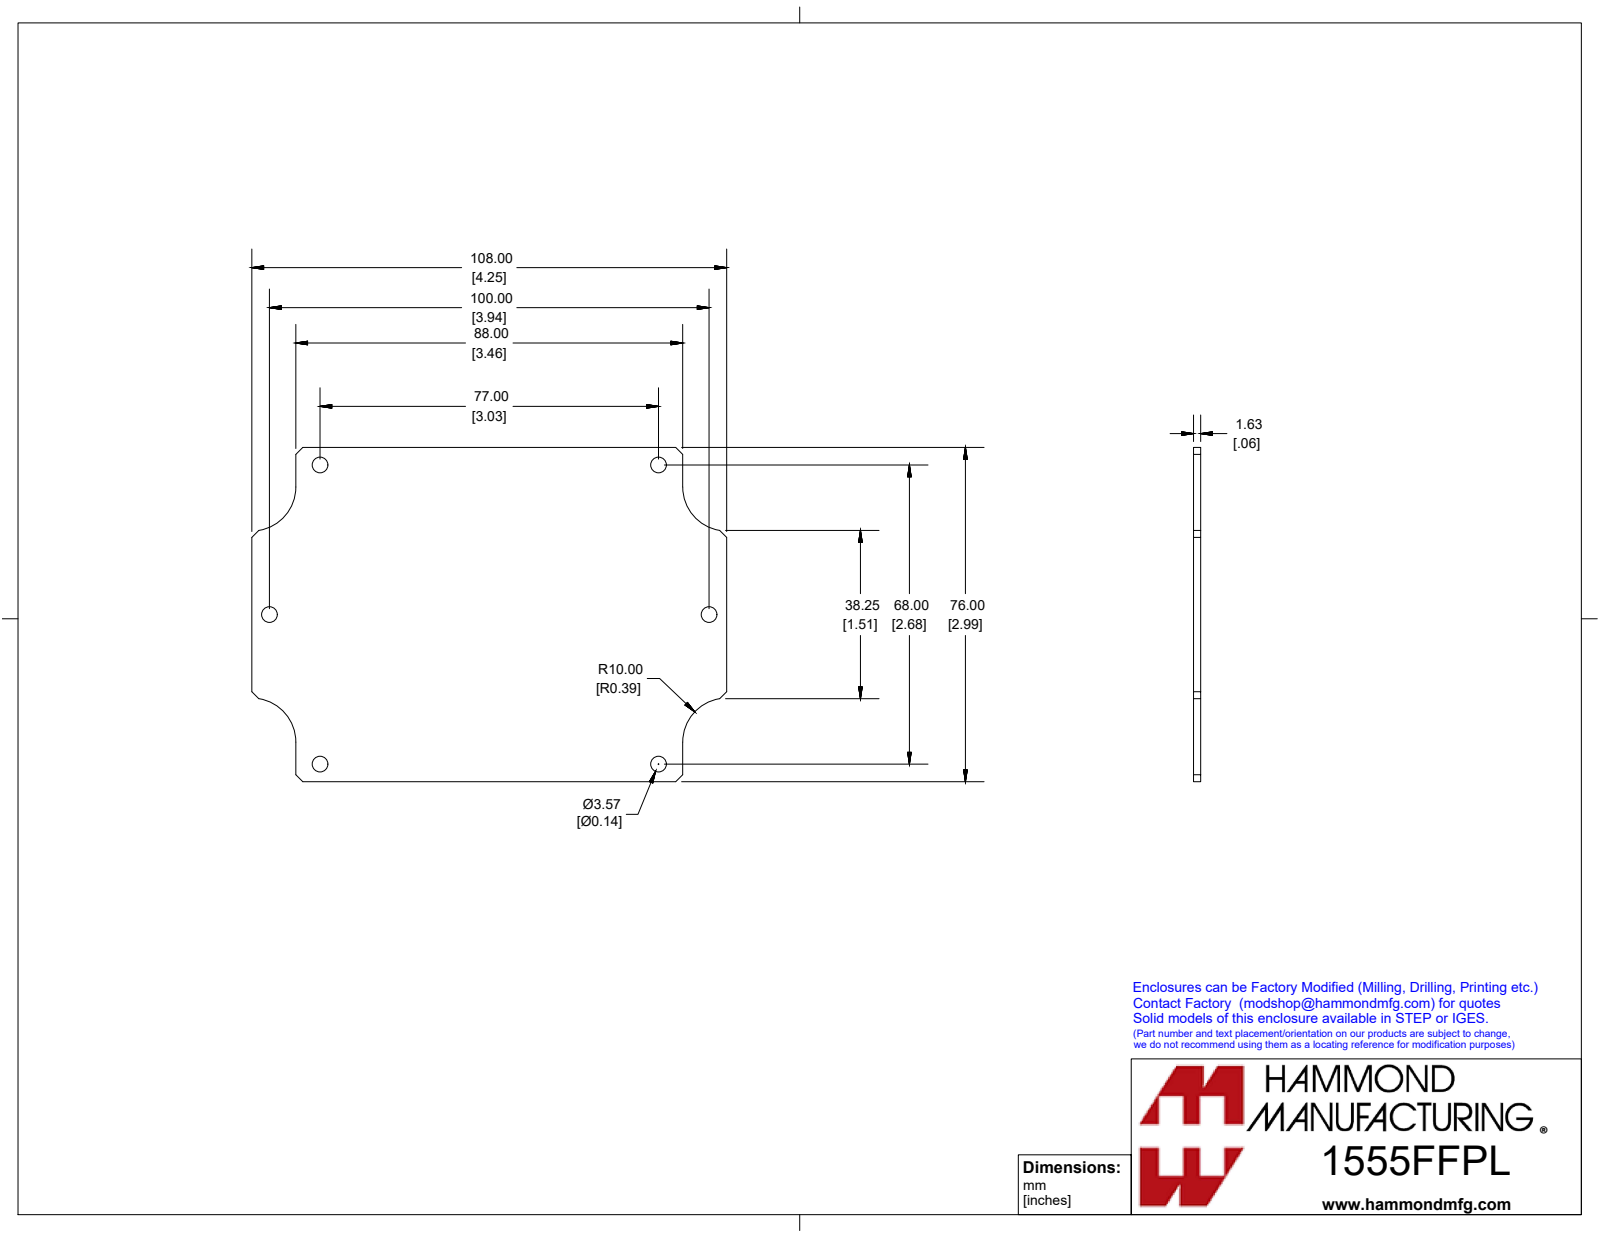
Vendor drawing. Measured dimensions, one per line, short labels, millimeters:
name: 1555FFPL
written by: SolidWorks 2019 (CONFIG_CONTROL_DESIGN)
unit: mm
bodies: 1 solid, 28 faces (18 planar, 10 cylindrical, 0 other)
size: 108 × 76 × 1.6
volume: 12 200 mm³; area: 15 610 mm²
holes: 6× ⌀3
rounds: 4× R10
face distances: 1.6, 76, 108, 10, 98, 88, 6.3, 107.4, 113.7, 101.2
hole spacings: 35.9, 94.8, 68, 77, 102.7, 100
